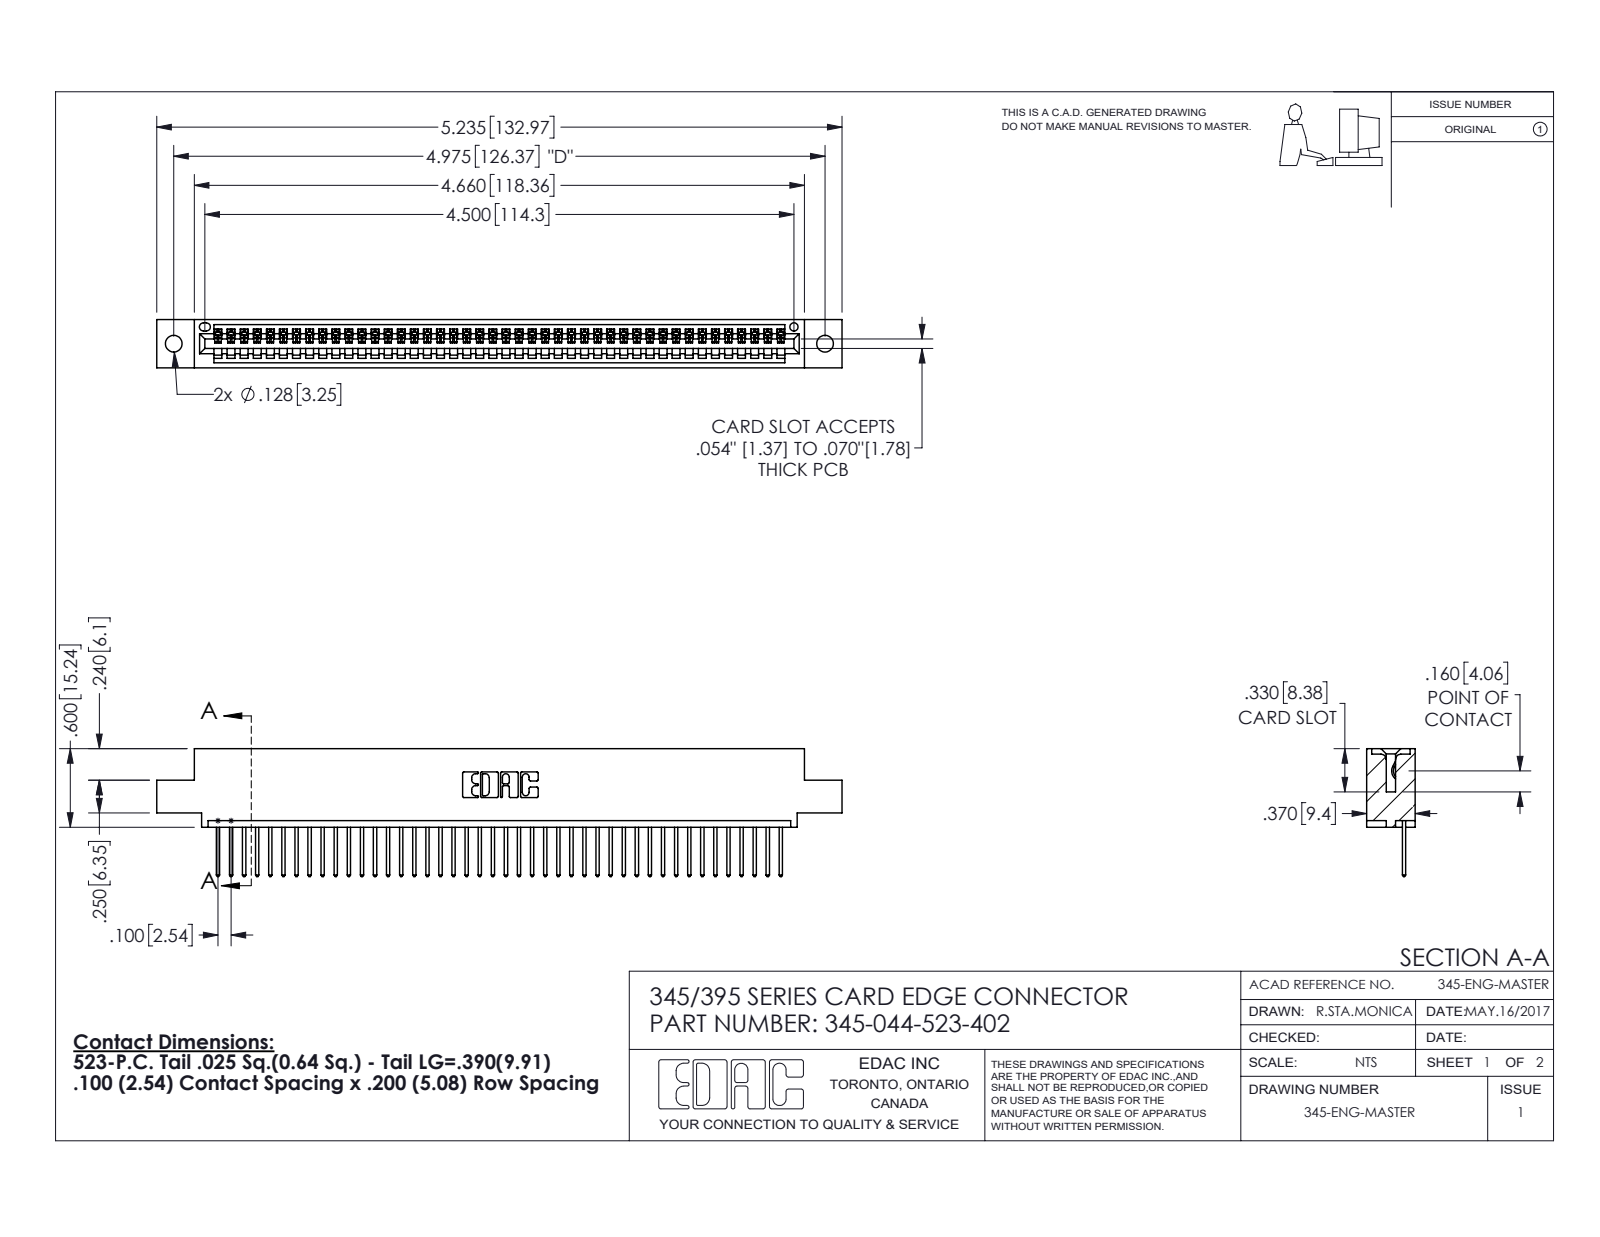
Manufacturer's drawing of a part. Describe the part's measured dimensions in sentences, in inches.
The part is named "345-292-001_345-293-123; 345-044-523-402; 345 Part_0.110 Offset - 0.128 Dia". Its 3-D file was written by "SolidWorks 2016 (CONFIG_CONTROL_DESIGN)". It is 45 solids with 2682 faces: 1844 planar, 838 cylindrical and 0 other. Overall it measures 5.235 by 0.977 by 0.37 inches. Its volume is 0.764 cubic inches and its surface area 25.61 square inches. Round holes: 2 of diameter 0.128, 1 of diameter 0.064. Partial cylindrical surfaces (rounded edges, fillets, slot ends): 88 of radius 0.006, 88 of radius 0.01, 22 of radius 0.01, 6 of radius 0.007, 6 of radius 0.031, 3 of radius 0.026, 2 of radius 0.031, 2 of radius 0.04. The main face-to-face distances are 0.072, 0.298, 0.37, 0.2, 0.098, 0.272, 0.025, 0.225, 0.149, 0.072. The hole center spacings are 0.27, 4.739, 4.975.
